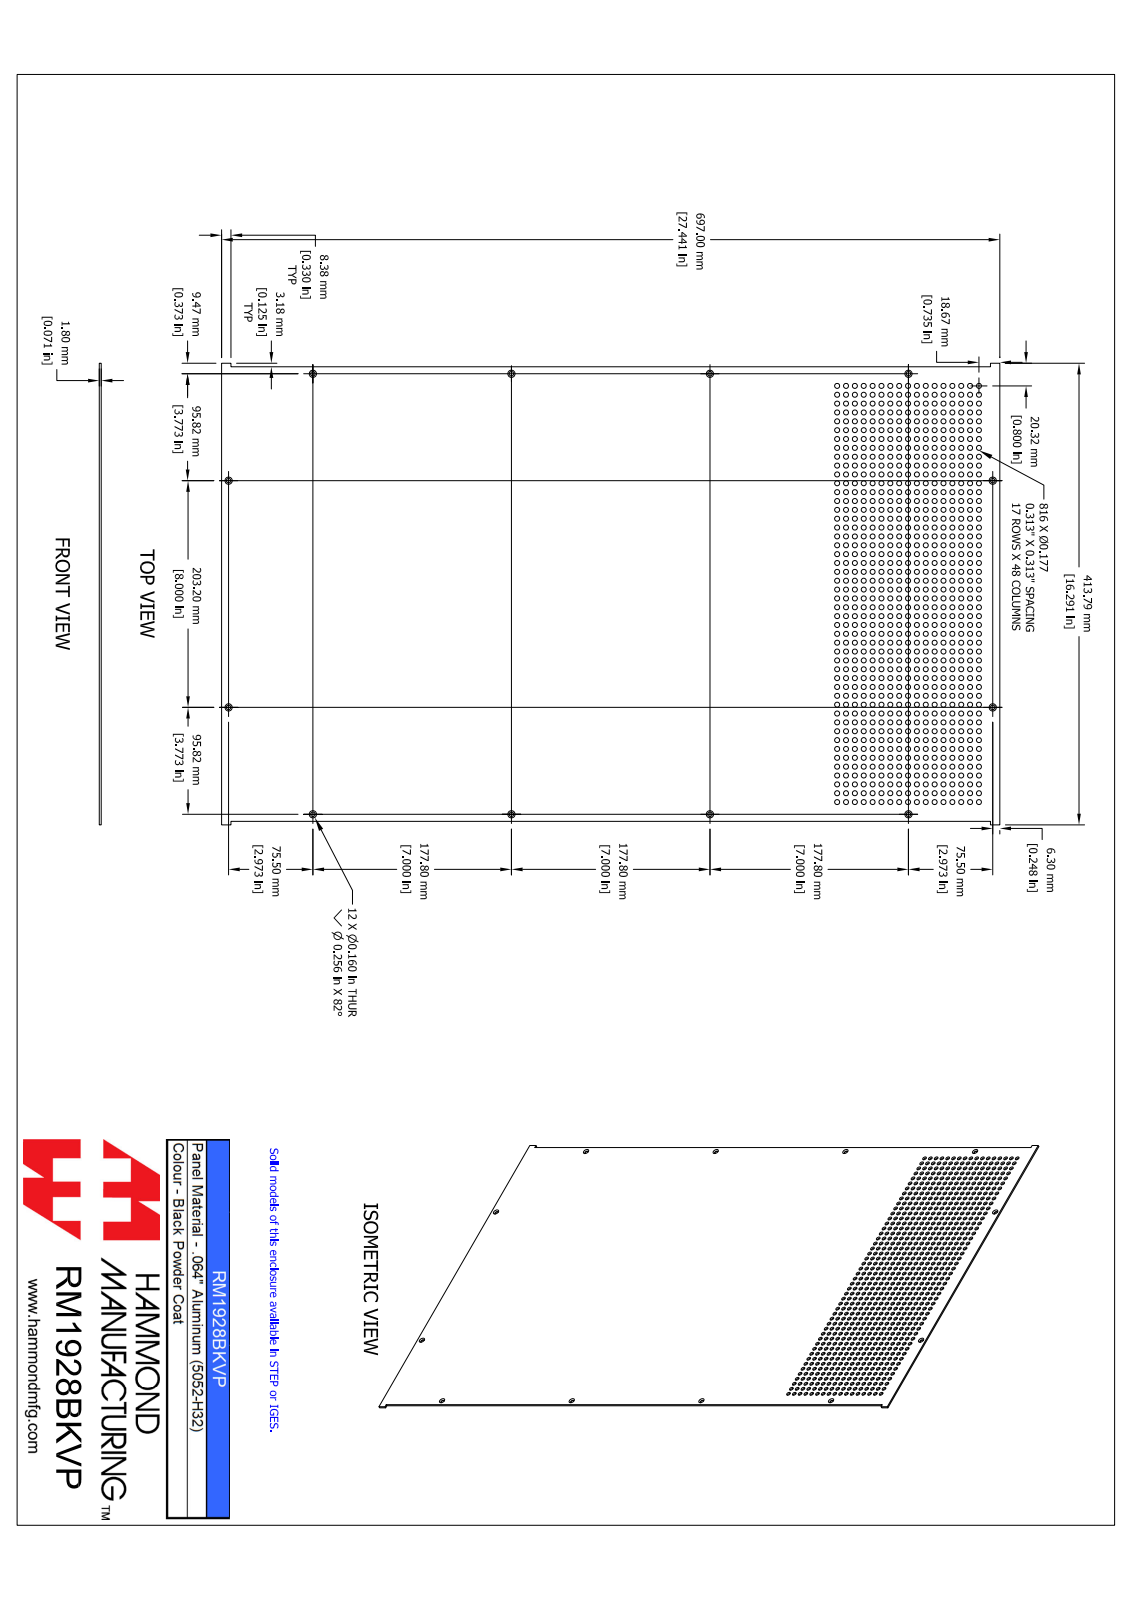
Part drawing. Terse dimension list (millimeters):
name: RM1928BKVP
written by: SolidWorks 2021 (AUTOMOTIVE_DESIGN)
unit: mm
bodies: 1 solid, 854 faces (14 planar, 828 cylindrical, 12 other)
size: 697 × 413.8 × 1.8
volume: 488 500 mm³; area: 567 000 mm²
holes: 816× ⌀4.5, 12× ⌀4.1
face distances: 1.8, 407.4, 697, 3.2, 410.6, 413.8, 8.4, 688.6, 680.2
hole spacings: 31.8, 8, 23.8, 39.7, 63.5, 15.9, 15.9, 55.5
